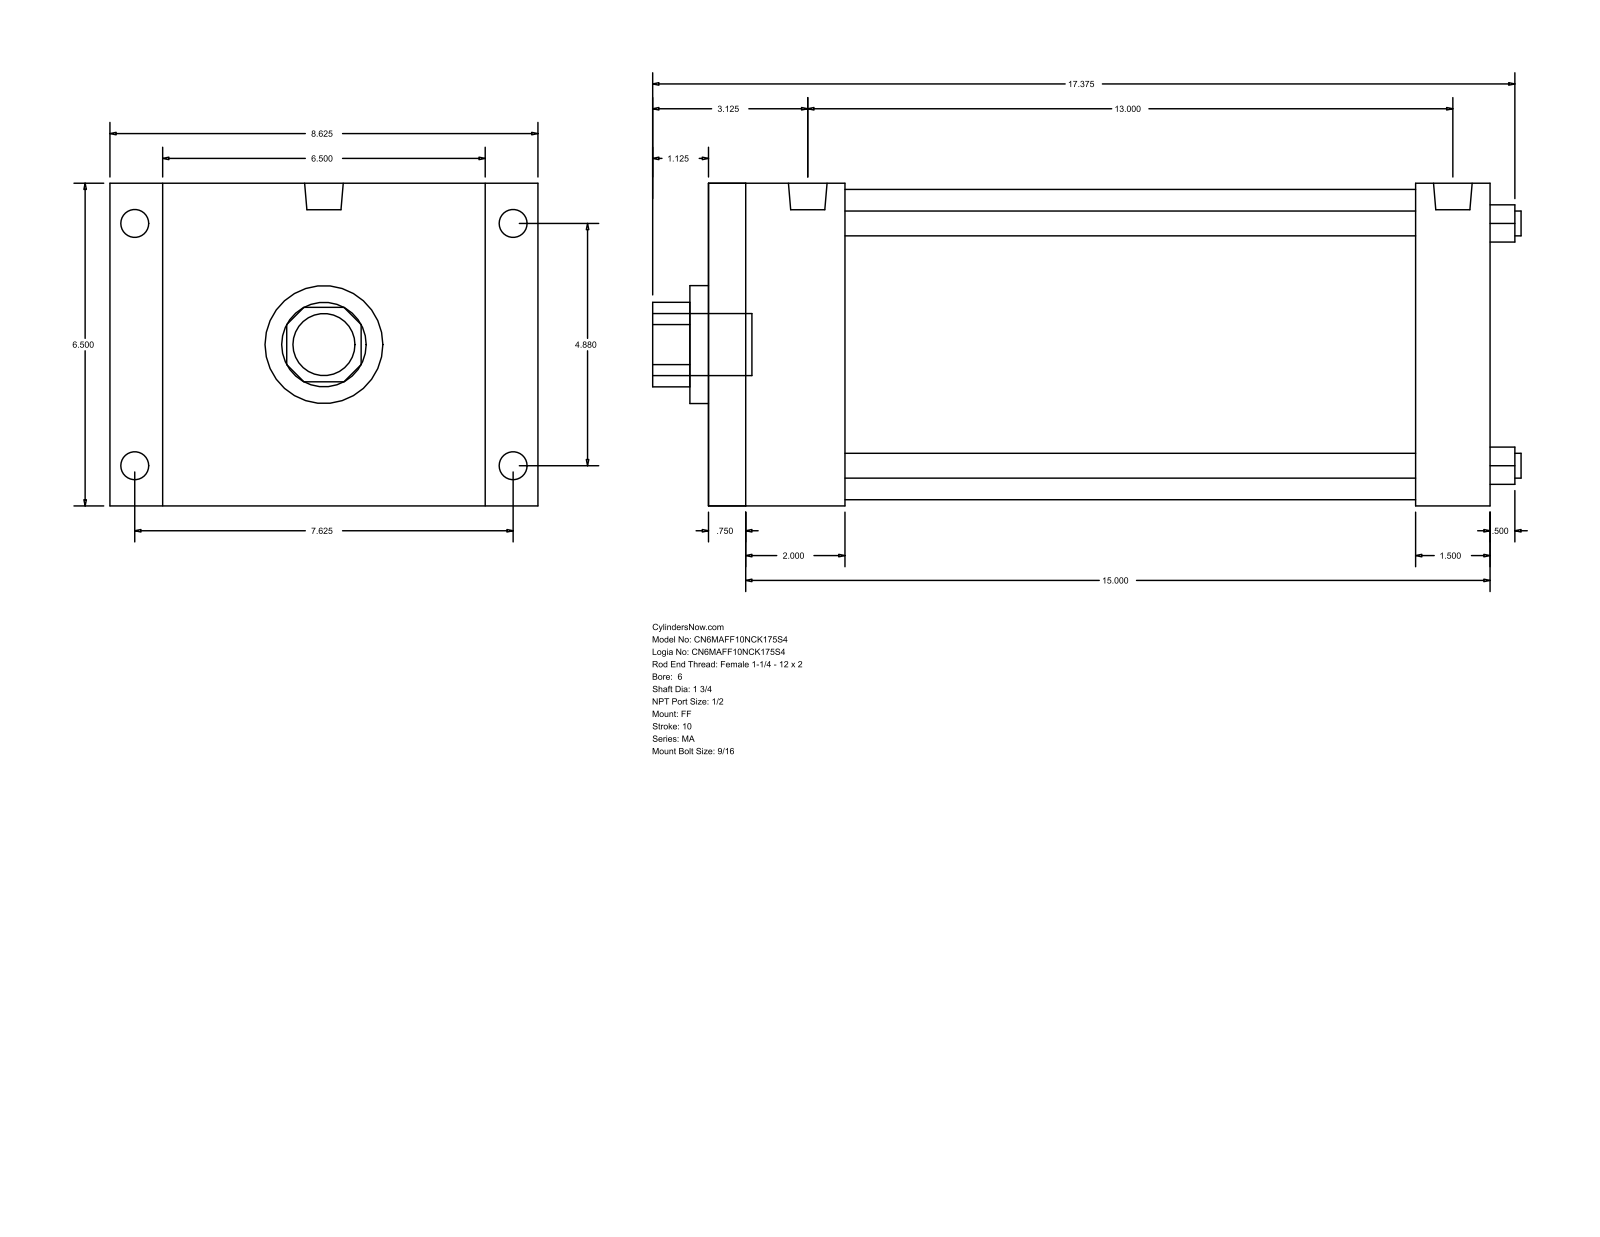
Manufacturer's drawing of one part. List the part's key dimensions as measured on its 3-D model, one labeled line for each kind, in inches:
Part name (STEP PRODUCT): MA_FF__0600_1.75
STEP written by: GSSL Pune (CONFIG_CONTROL_DESIGN)
Units: inches
Bodies: 0 solids, 92 faces (64 planar, 28 cylindrical, 0 other)
Overall size (bounding box): 17.5 × 8.625 × 6.5
Round holes (diameter × count): ⌀0.5 ×4, ⌀1.75 ×1, ⌀2.375 ×1, ⌀6.25 ×1
Round bosses / shafts (diameter × count): ⌀0.687 ×4, ⌀0.563 ×4, ⌀0.778 ×2, ⌀1.25 ×1
Partial cylindrical surfaces — rounded edges, fillets, slot ends (radius × count): R0.852 ×1
Main face-to-face distances: 6.5, 15.75, 0.75, 15, 2, 13.5, 1.5, 2.75, 13, 14.25
Hole centre spacings: 3.451, 4.88, 6.902
